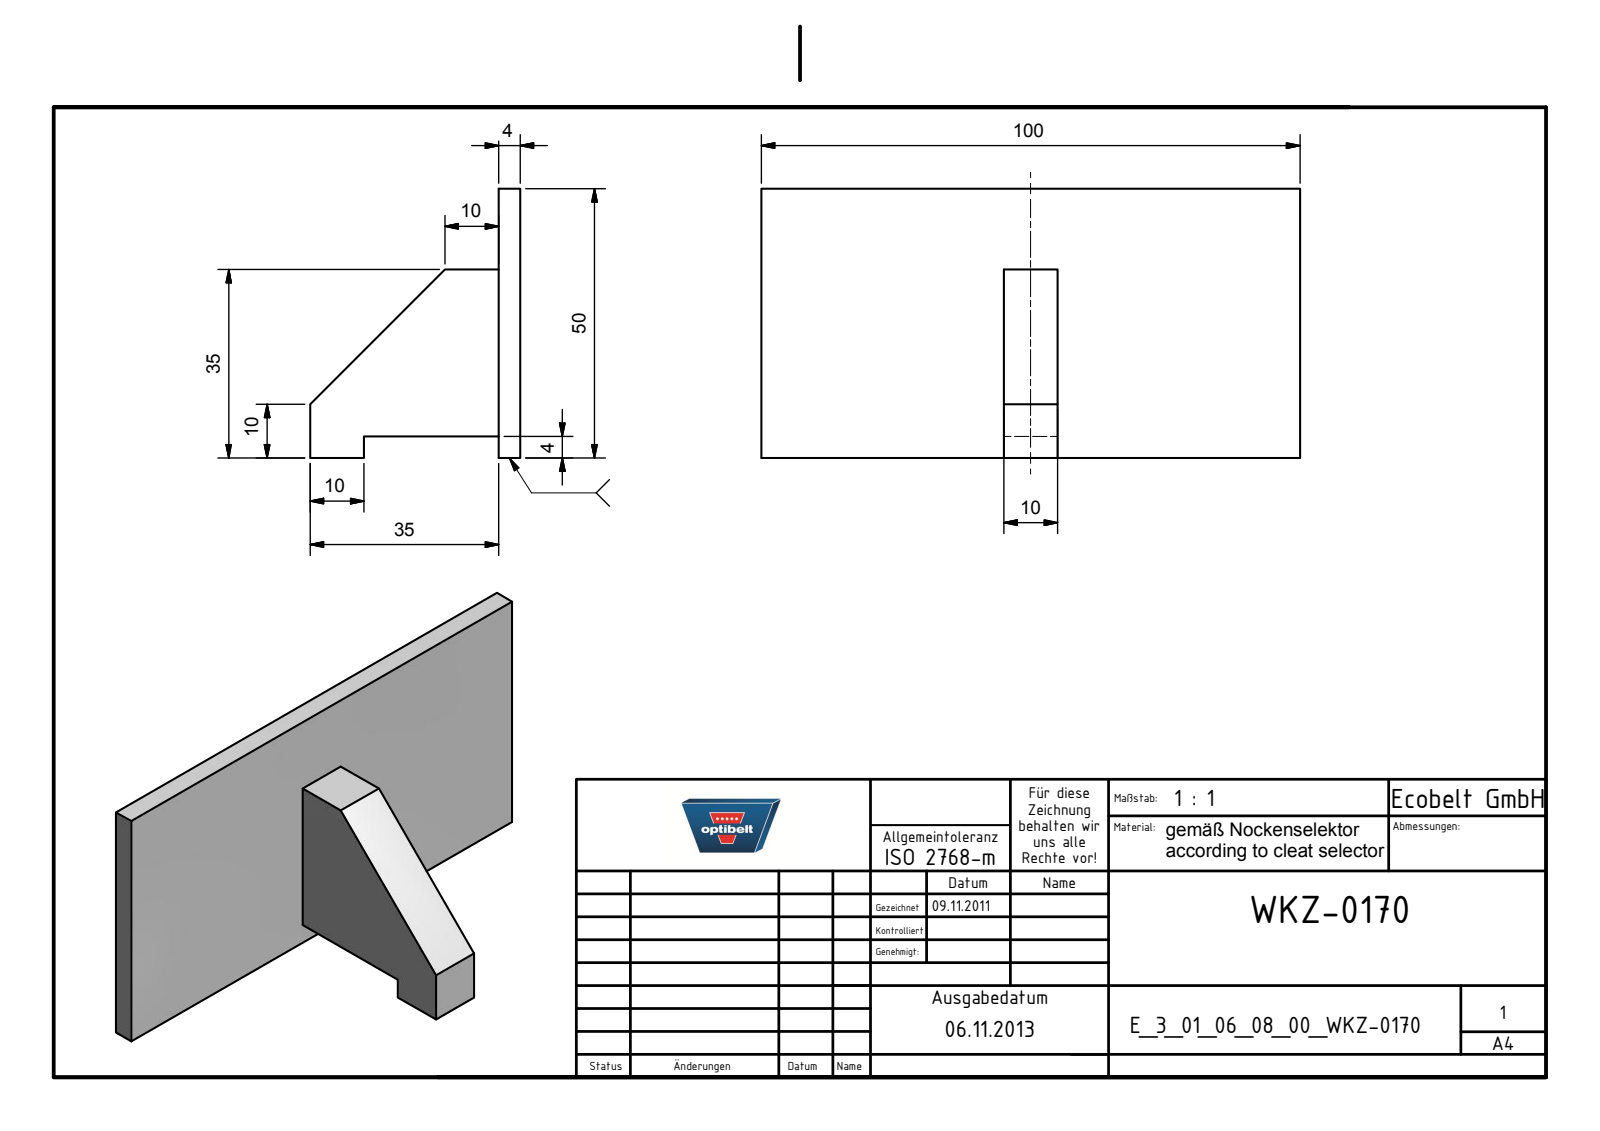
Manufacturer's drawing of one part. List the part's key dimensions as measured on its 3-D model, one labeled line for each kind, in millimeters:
Part name (STEP PRODUCT): E_3_01_06_08_00_WKZ-0170
STEP written by: Autodesk Inventor 2025 (AUTOMOTIVE_DESIGN)
Units: millimetres
Bodies: 1 solid, 14 faces (14 planar, 0 cylindrical, 0 other)
Overall size (bounding box): 100 × 50 × 39
Volume: 28 125 mm³ · Surface area: 13 459 mm²
Main face-to-face distances: 4, 10, 50, 45, 55, 46, 100, 35, 39, 31
